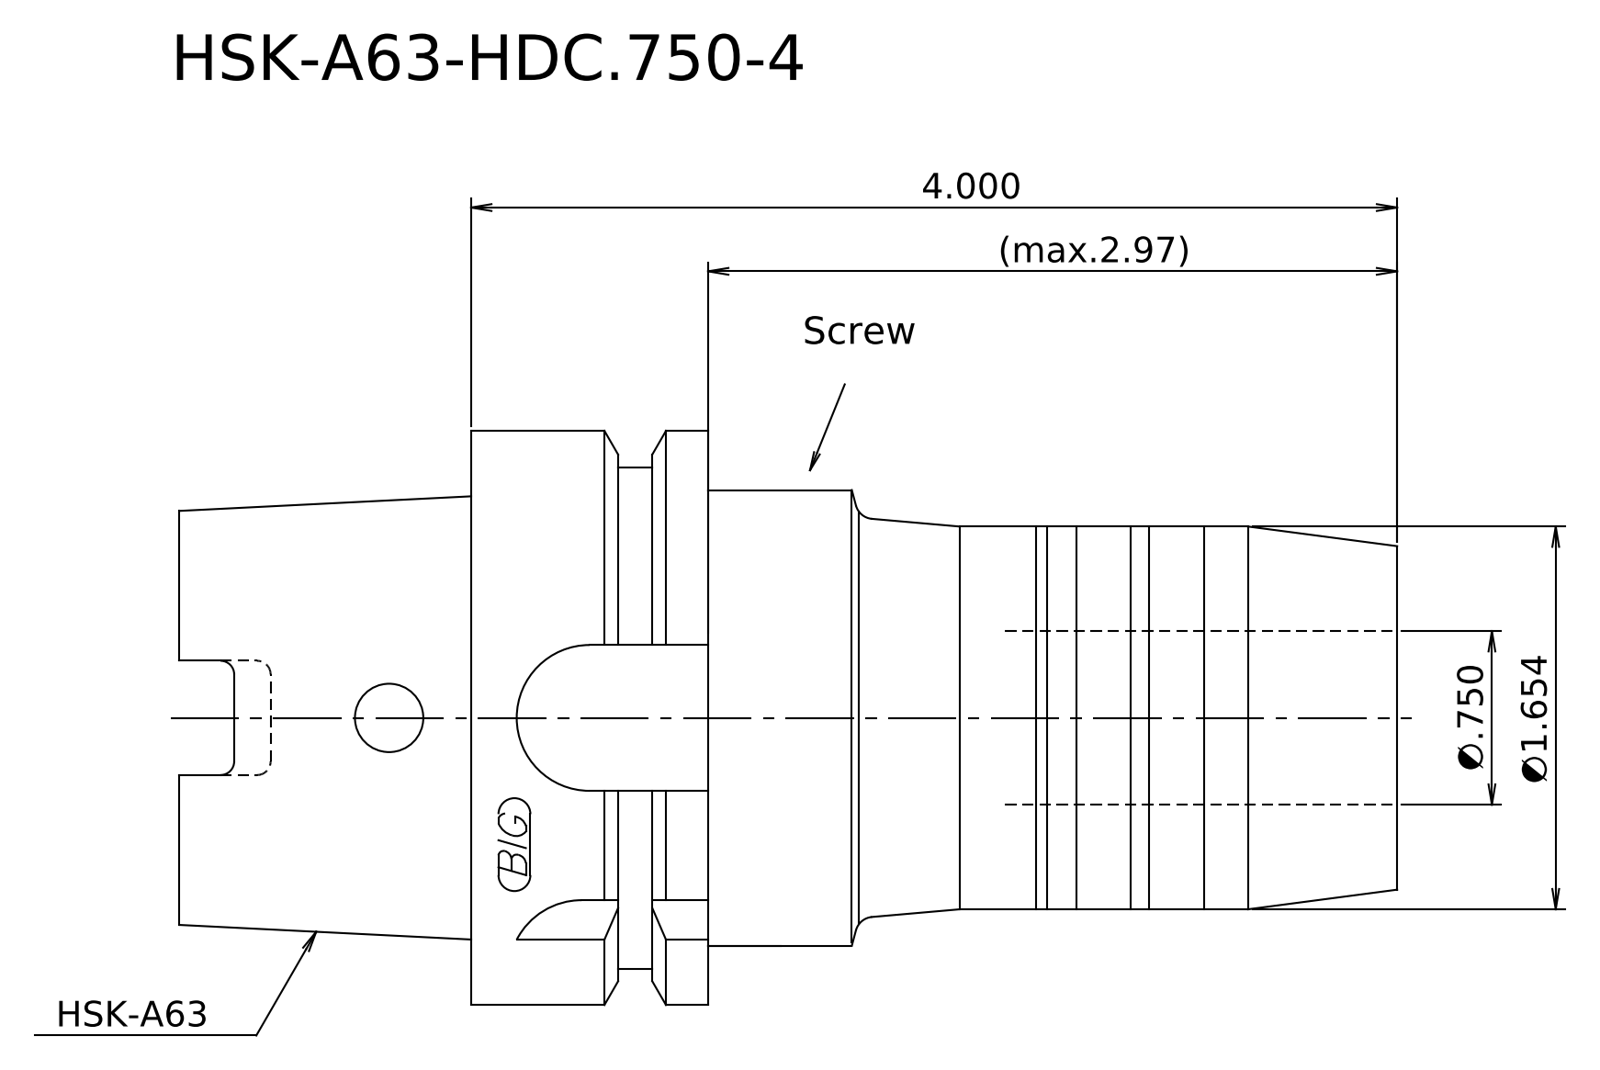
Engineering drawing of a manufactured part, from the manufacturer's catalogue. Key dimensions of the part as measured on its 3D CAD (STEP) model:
STEP written by: Kubotek KeyCreator 2011 V10.0.2 (22737) (automotive_design)
Units: millimetres
Bodies: 1 solid, 17 faces (6 planar, 5 cylindrical, 6 other)
Overall size (bounding box): 133.6 × 63 × 63
Volume: 246 030 mm³ · Surface area: 26 562 mm²
Round bosses / shafts (diameter × count): ⌀63 ×1, ⌀55 ×1, ⌀50 ×1, ⌀42 ×1
Main face-to-face distances: 32, 26, 58, 75.6, 101.6, 133.6, 81.72, 6.12, 19.88, 51.88
